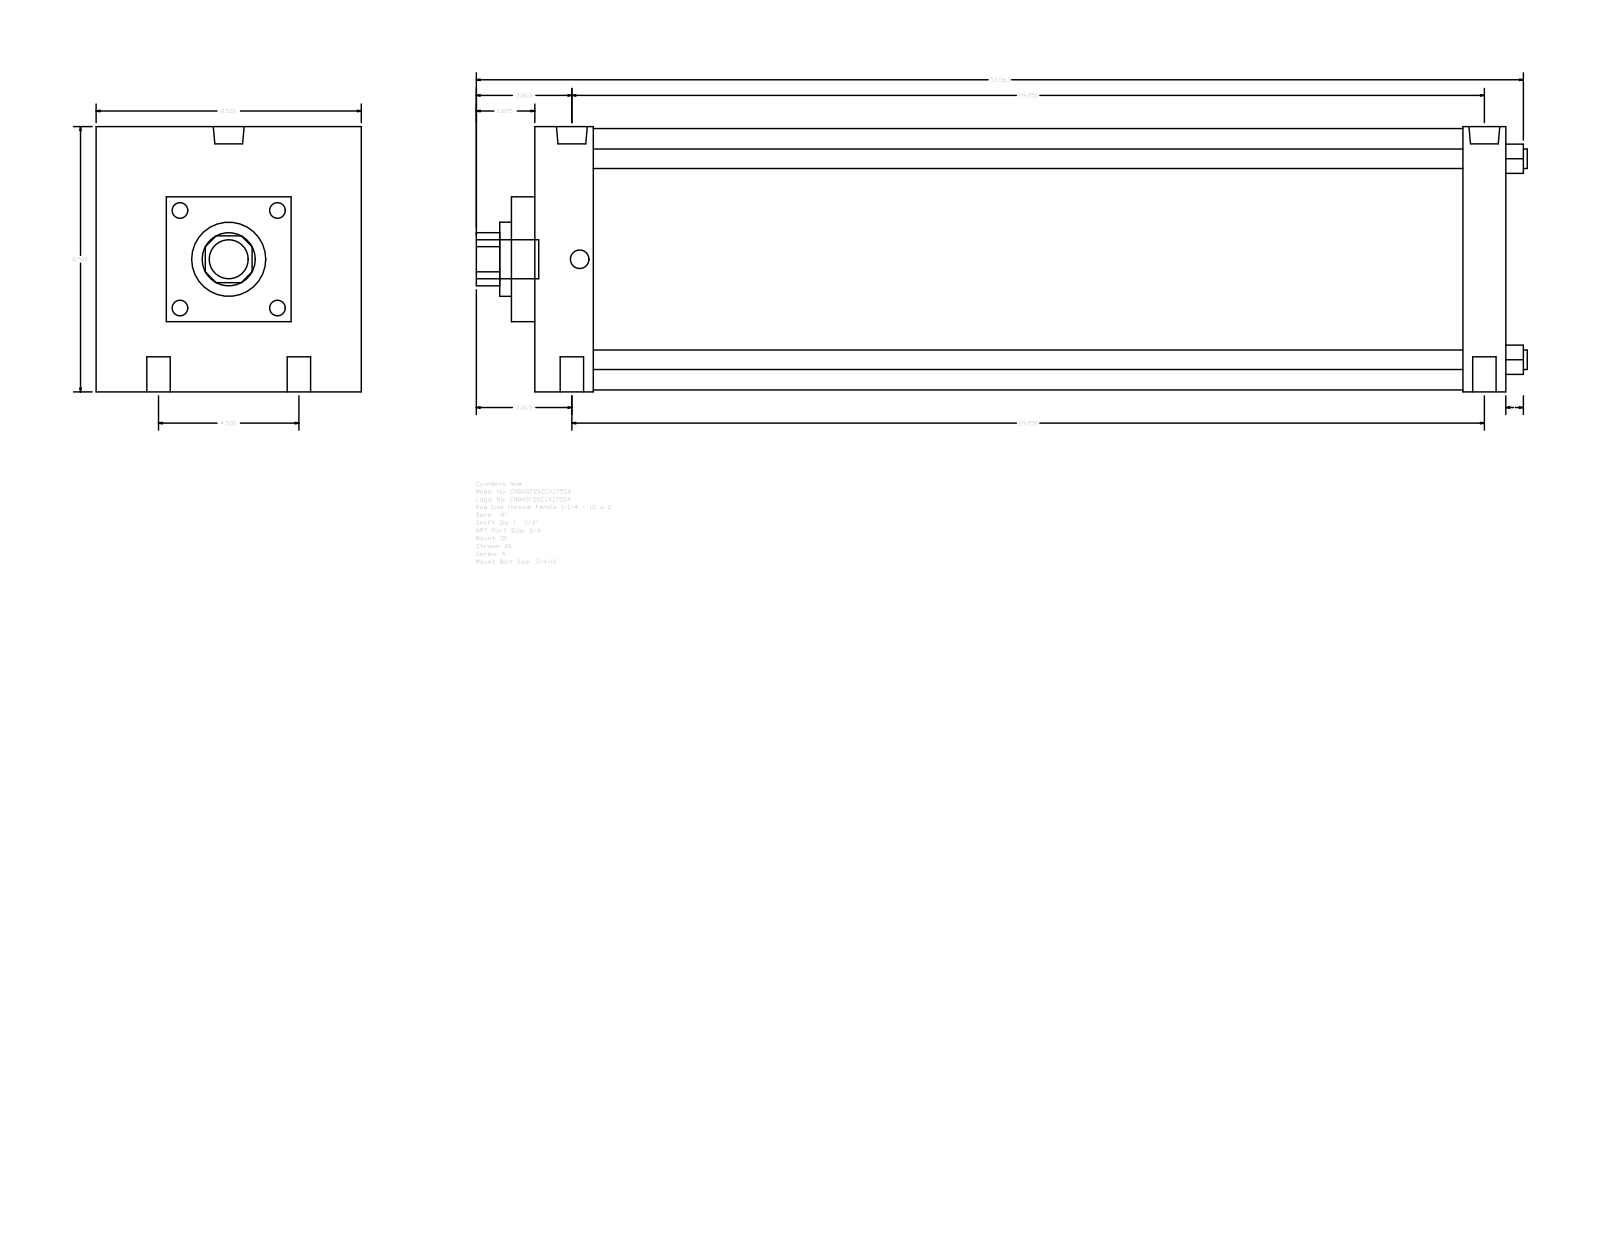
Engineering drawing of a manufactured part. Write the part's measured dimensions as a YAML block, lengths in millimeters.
part_name: "A_SF__0800_1.75"
step_written_by: "GSSL Pune (CONFIG_CONTROL_DESIGN)"
units: millimeters
bodies: {solids: 0, faces: 93, planar: 67, cylindrical: 26, other: 0}
overall_size: [855.66, 215.9, 215.9]
round_holes:
  - {diameter: 19.05, count: 4}
  - {diameter: 15.08, count: 2}
  - {diameter: 25.12, count: 2}
  - {diameter: 44.45, count: 1}
  - {diameter: 60.33, count: 1}
round_bosses_or_shafts:
  - {diameter: 15.88, count: 4}
  - {diameter: 212.72, count: 1}
  - {diameter: 31.75, count: 1}
partial_cylinders:
  - {radius: 21.63, count: 1}
face_to_face_distances: [790.58, 215.9, 47.63, 755.65, 708.02, 742.95, 34.93, 19.05, 158.75, 57.15]
hole_center_spacings: [57.15, 745.14, 742.95, 114.3, 751.69, 730.25]
